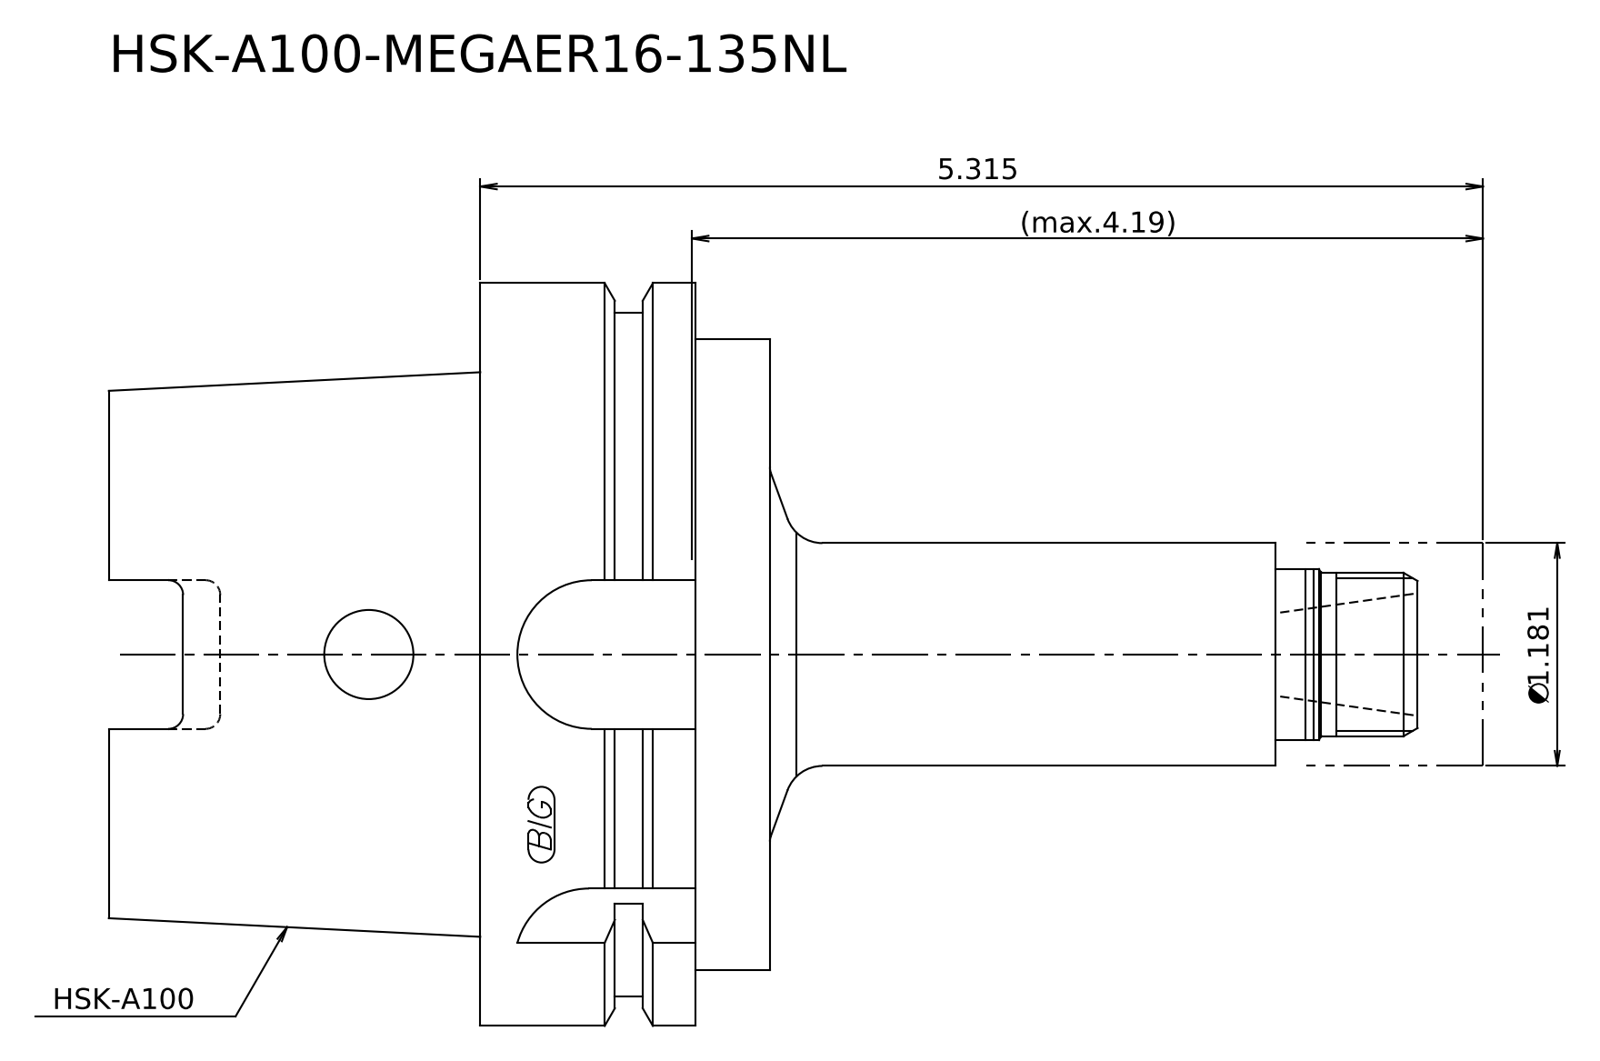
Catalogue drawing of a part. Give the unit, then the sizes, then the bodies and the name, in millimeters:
Units: millimetres
Overall size (bounding box): 185 × 100 × 100
Round bosses / shafts (diameter × count): ⌀100 ×1, ⌀92 ×1, ⌀85 ×1, ⌀30 ×1, ⌀23 ×1, ⌀22 ×1
Main face-to-face distances: 89, 39, 50, 10, 29, 79, 71, 81, 110, 160
Volume: 568 553 mm³ · Surface area: 51 220 mm²
Bodies: 2 solids, 24 faces (10 planar, 8 cylindrical, 6 other)
STEP written by: Kubotek KeyCreator 2011 V10.0.2 (22737) (automotive_design)
